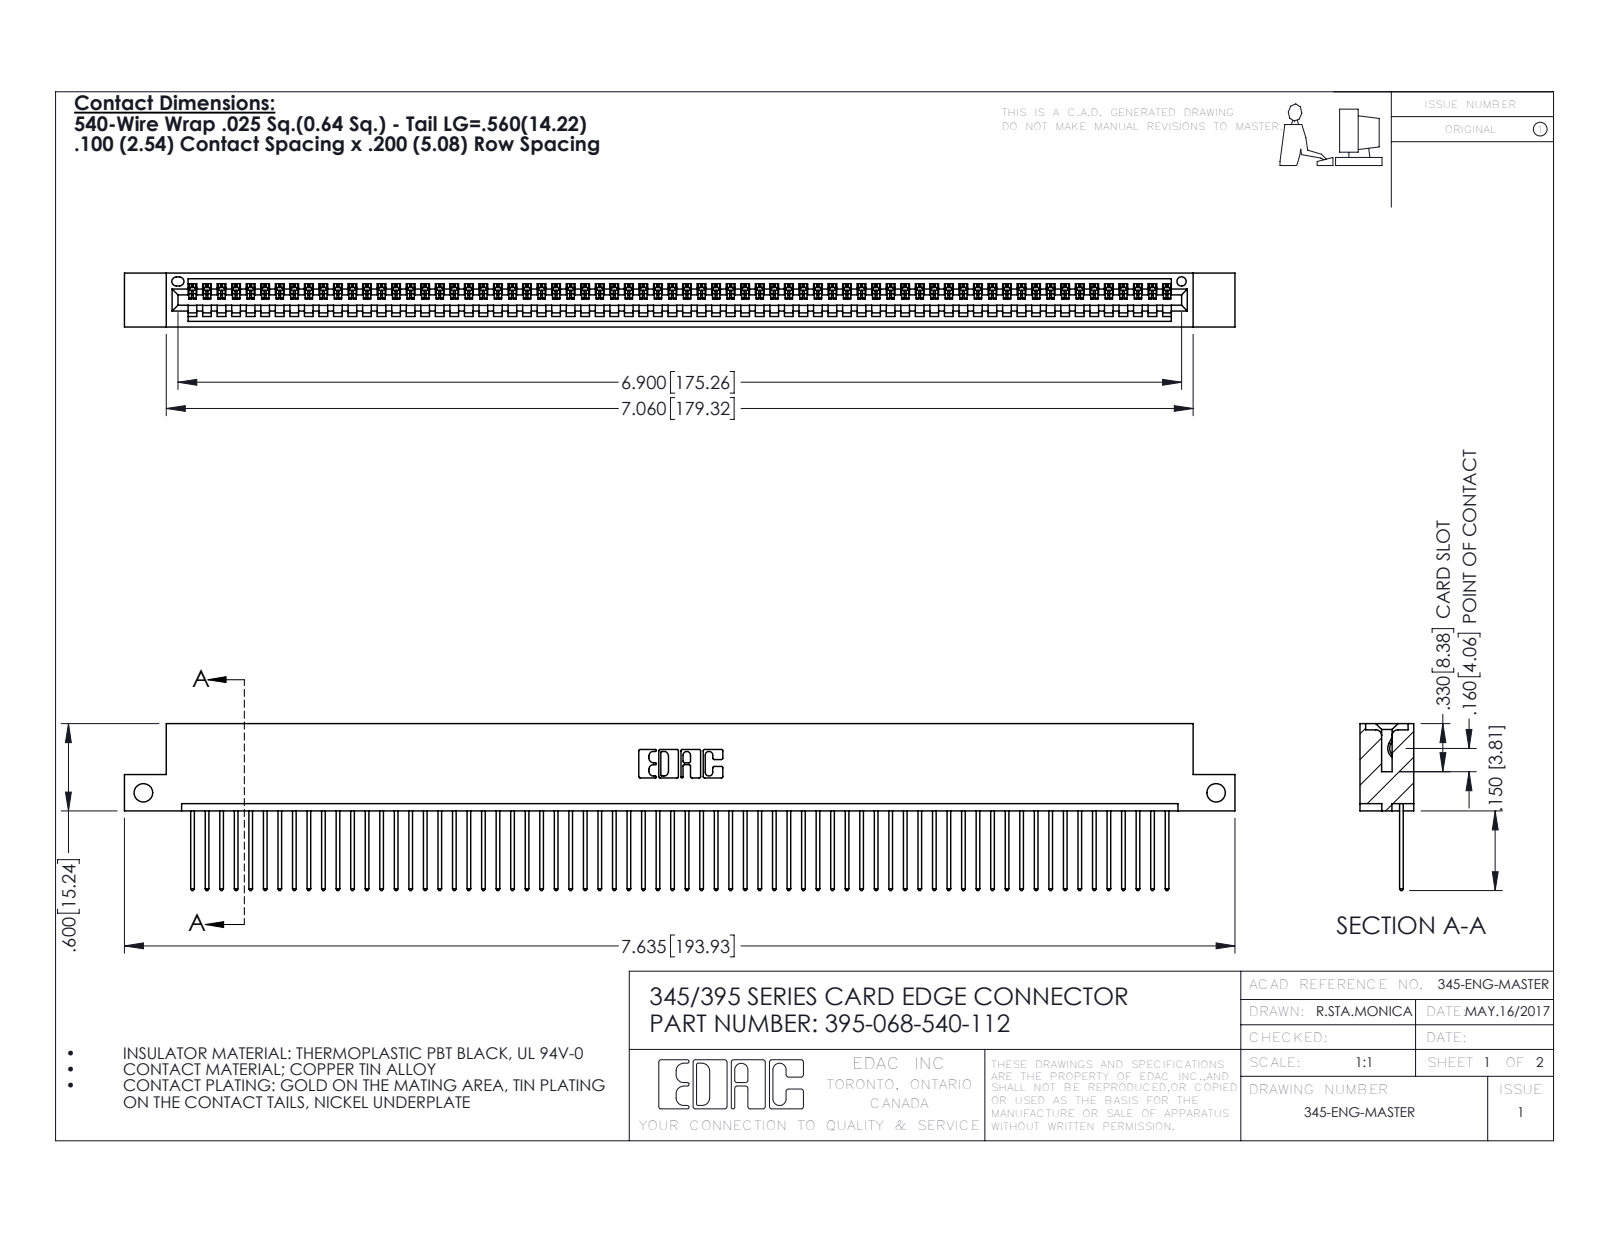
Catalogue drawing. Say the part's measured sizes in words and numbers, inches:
The part is named "395-068-540-112; 345 Part_Flush Mounting Lugs - Side Mount; 345-292-001_345-293-140". Its 3-D file was written by "SolidWorks 2016 (CONFIG_CONTROL_DESIGN)". It is 69 solids with 4070 faces: 2800 planar, 1270 cylindrical and 0 other. Overall it measures 7.635 by 1.147 by 0.37 inches. Its volume is 1.137 cubic inches and its surface area 39.74 square inches. Round holes: 2 of diameter 0.128, 1 of diameter 0.064. Partial cylindrical surfaces (rounded edges, fillets, slot ends): 136 of radius 0.006, 136 of radius 0.01, 22 of radius 0.01, 6 of radius 0.007, 6 of radius 0.031, 3 of radius 0.026, 2 of radius 0.031, 2 of radius 0.04. The main face-to-face distances are 0.072, 0.298, 0.37, 0.098, 0.272, 0.025, 0.2, 0.225, 0.149, 0.072. The hole center spacings are 7.375.
